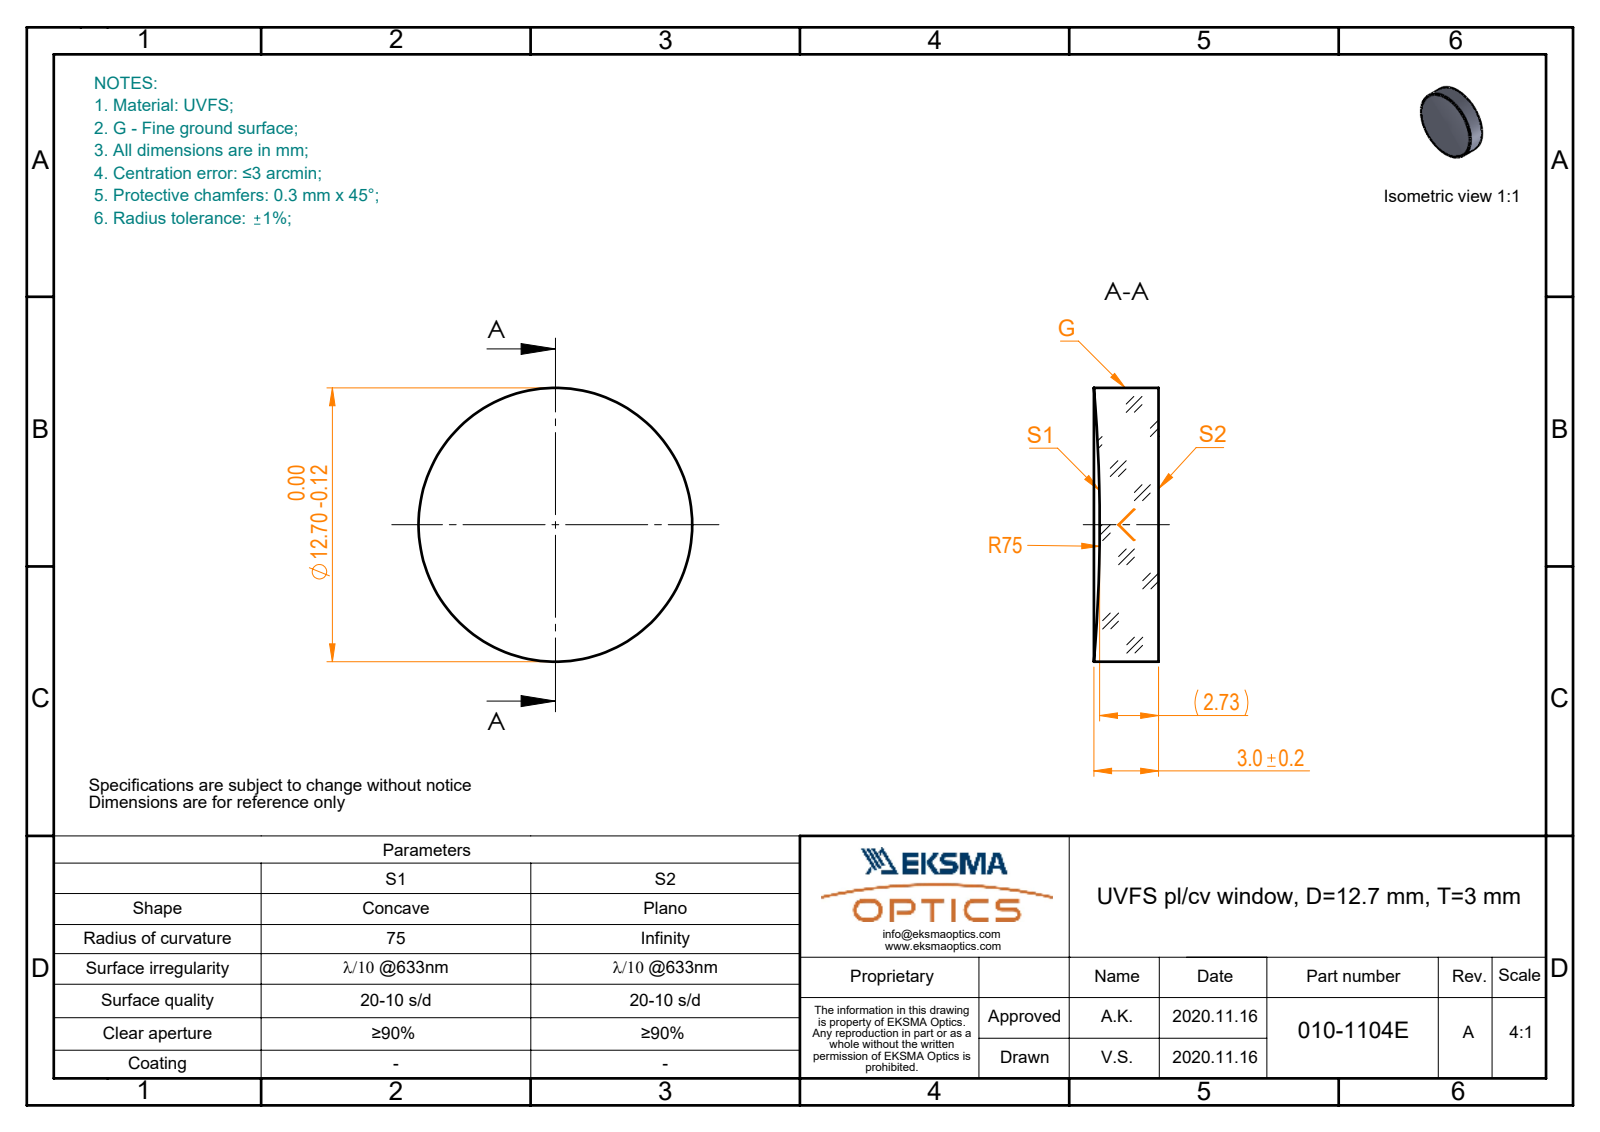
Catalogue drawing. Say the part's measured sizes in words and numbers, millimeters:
The part is named "010-1104E_UVFS_PCV_window". Its 3-D file was written by "SolidWorks 2019 (CONFIG_CONTROL_DESIGN)". It is 1 solid with 5 faces: 1 planar, 2 cylindrical and 2 other. Overall it measures 12.7 by 12.7 by 3 millimeters. Its volume is 363 cubic millimeters and its surface area 373 square millimeters. Round bosses or shafts: 1 of diameter 12.7.
